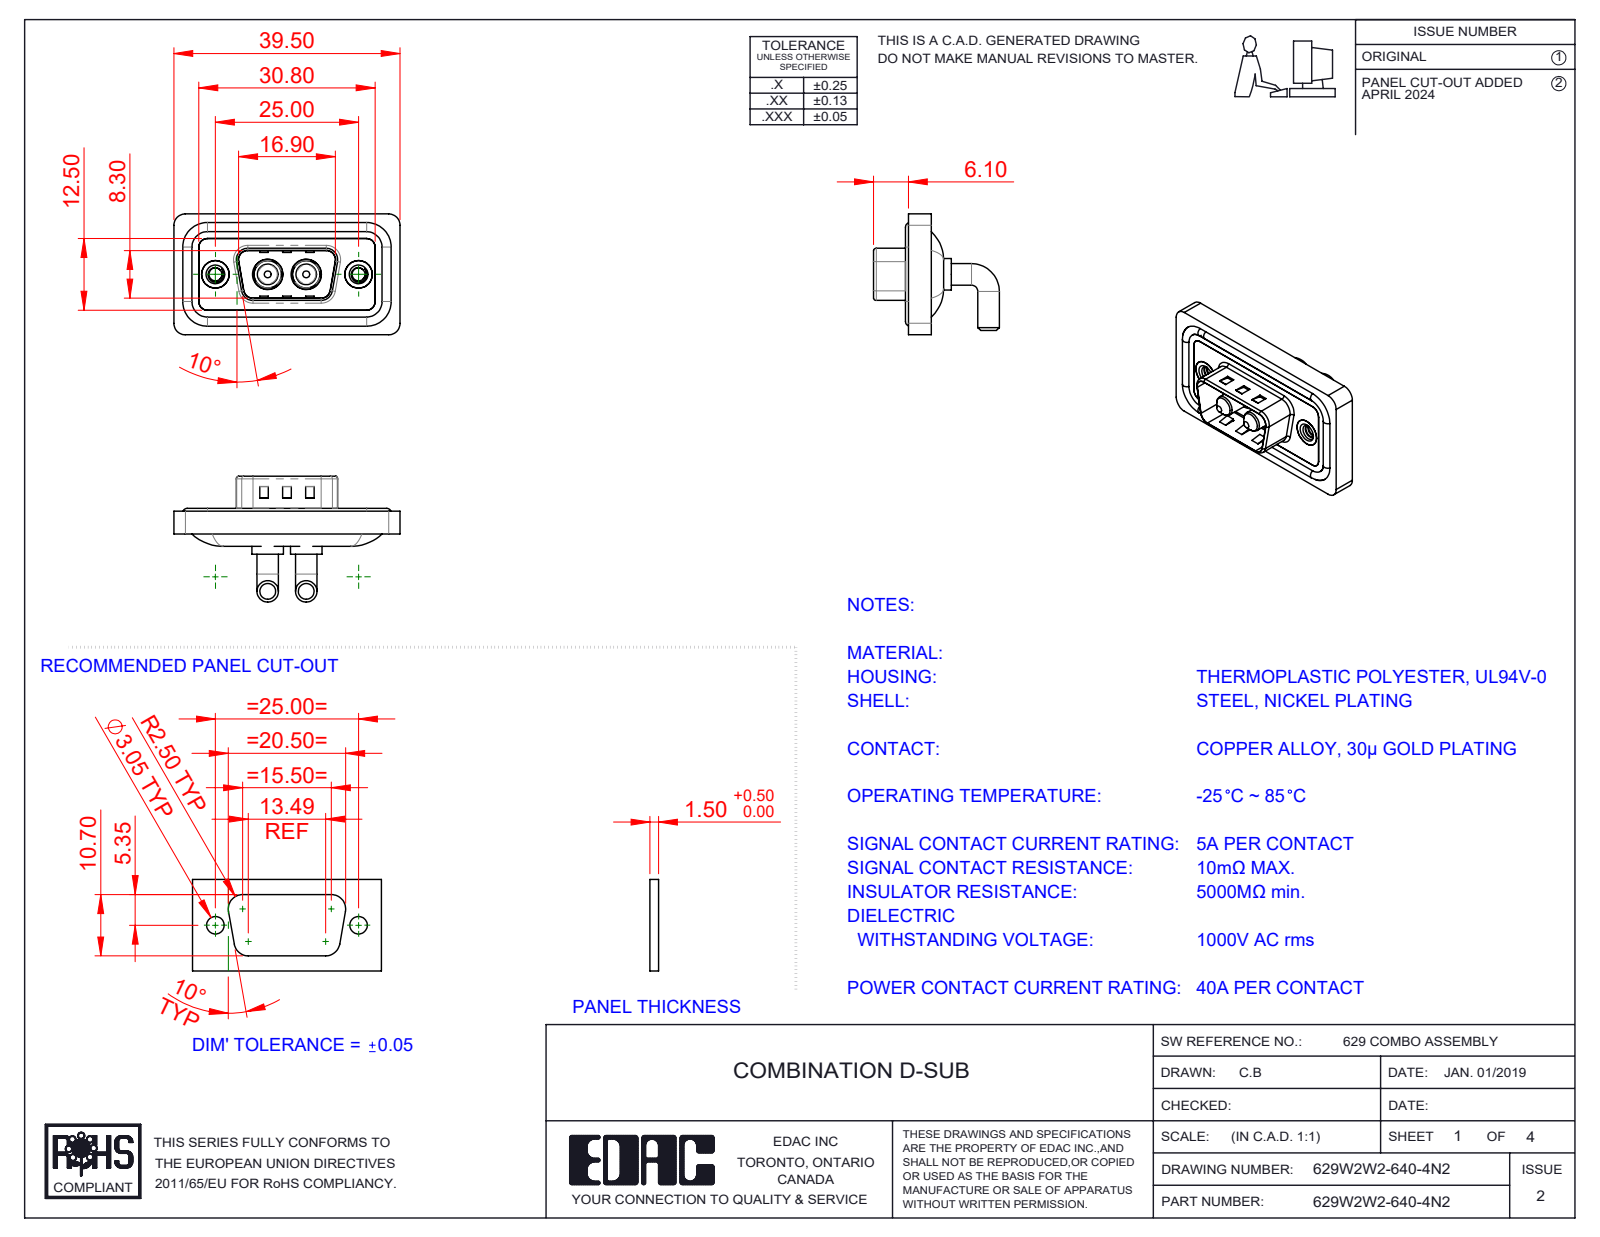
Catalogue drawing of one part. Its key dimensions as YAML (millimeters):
part_name: "629Combo Threaded Rivet_2; 629Combo Shell Front_09 Contacts; 629Combo Housing_2W2; 629Combo Shell Rear_09 Contacts (+3 more)"
step_written_by: "SolidWorks 2023 (CONFIG_CONTROL_DESIGN)"
units: millimeters
bodies: {solids: 11, faces: 497, planar: 165, cylindrical: 222, other: 110}
overall_size: [39.5, 21.98, 21.1]
volume: 4741
surface_area: 7255
round_holes:
  - {diameter: 2.26, count: 2}
  - {diameter: 4, count: 2}
  - {diameter: 4.8, count: 2}
  - {diameter: 4.85, count: 2}
  - {diameter: 5, count: 2}
  - {diameter: 5.3, count: 2}
round_bosses_or_shafts:
  - {diameter: 3.75, count: 4}
  - {diameter: 1.6, count: 4}
  - {diameter: 5.5, count: 2}
  - {diameter: 5.2, count: 2}
  - {diameter: 4.9, count: 2}
  - {diameter: 4.75, count: 2}
  - {diameter: 3.6, count: 2}
partial_cylinders:
  - {radius: 1.5, count: 18}
  - {radius: 2, count: 18}
  - {radius: 0.5, count: 8}
  - {radius: 1.6, count: 8}
  - {radius: 0.25, count: 4}
  - {radius: 0.6, count: 4}
  - {radius: 0.65, count: 4}
  - {radius: 0.9, count: 4}
face_to_face_distances: [0.4, 2.9, 1.1, 0.8, 2.1, 2.5, 3.1, 1.6, 4.5, 1.5]
hole_center_spacings: [9.14, 15.86, 6.72, 25]
